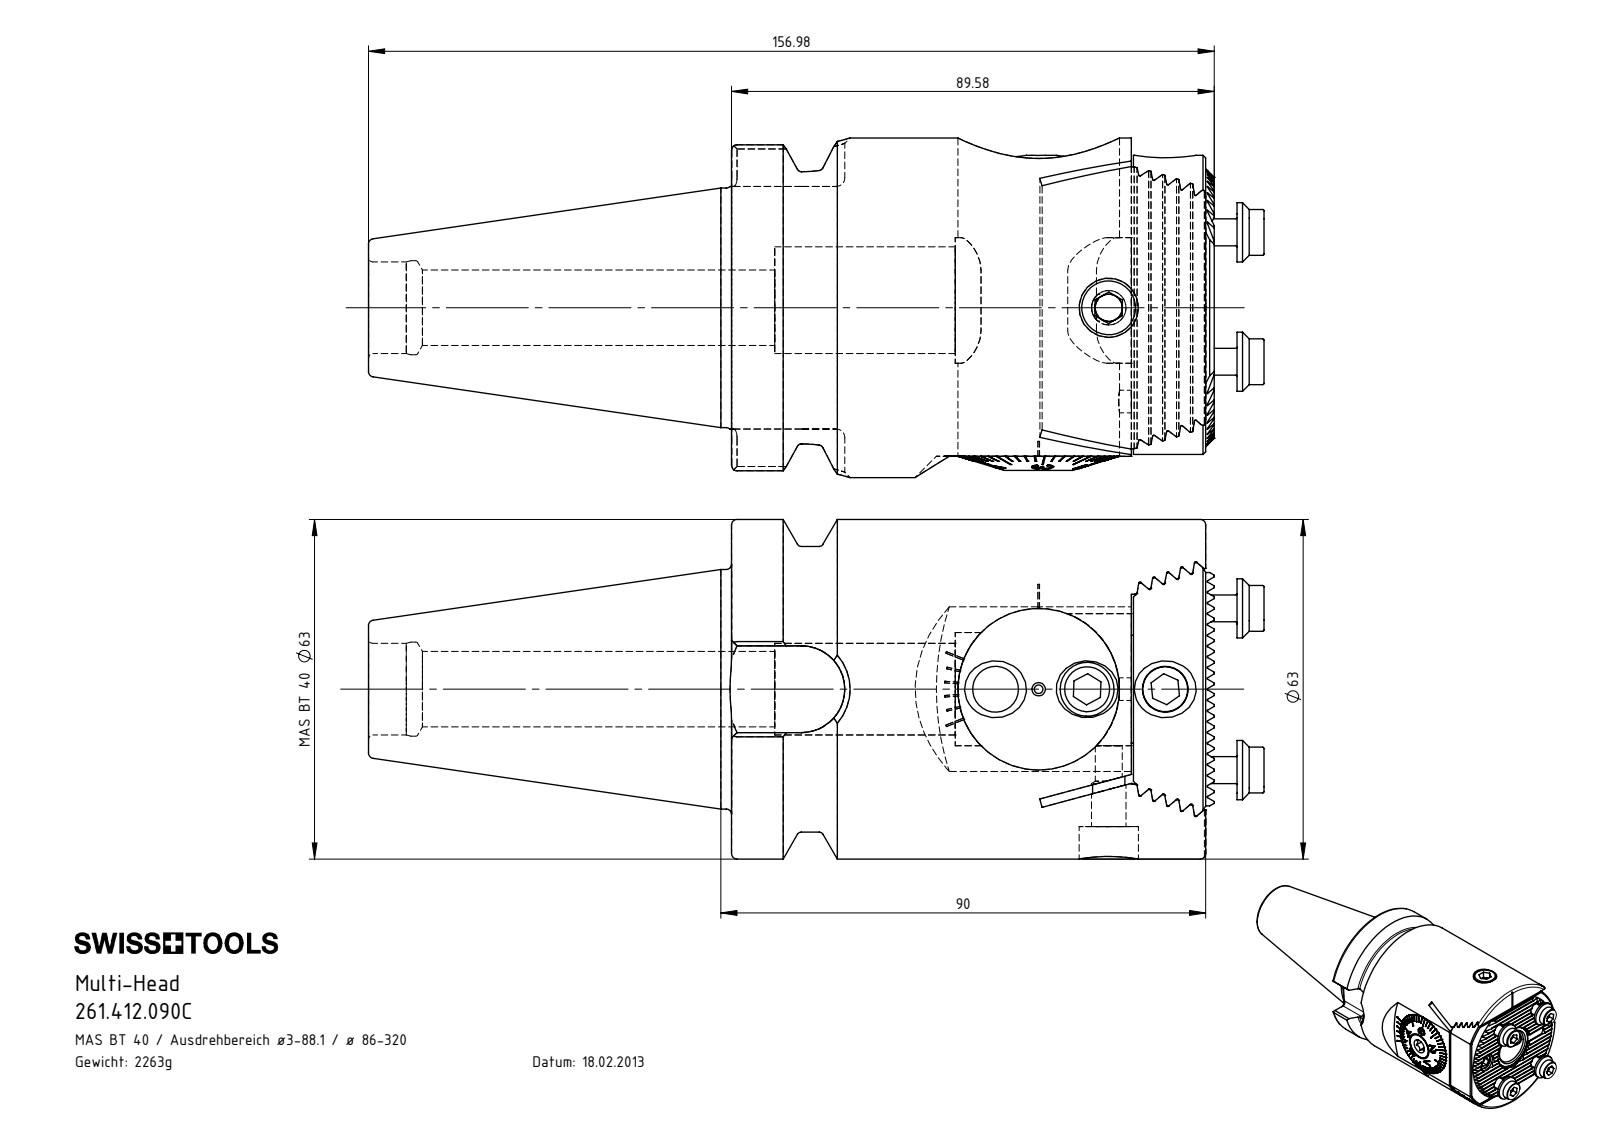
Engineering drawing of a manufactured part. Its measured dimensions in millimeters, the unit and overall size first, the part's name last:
Units: millimetres
Overall size (bounding box): 166.24 × 63 × 63
Round holes (diameter × count): ⌀4.2 ×5, ⌀8.5 ×4, ⌀6.8 ×3, ⌀11 ×3, ⌀14 ×2, ⌀20 ×2, ⌀1 ×1, ⌀1.6 ×1, ⌀3.3 ×1, ⌀5 ×1, ⌀6.4 ×1, ⌀8 ×1
Round bosses / shafts (diameter × count): ⌀11 ×4, ⌀8.5 ×4, ⌀5 ×4, ⌀10 ×3, ⌀63 ×1, ⌀53 ×1, ⌀44.45 ×1, ⌀30 ×1
Partial cylindrical surfaces — rounded edges, fillets, slot ends (radius × count): R0.14 ×21, R0.2 ×20, R1.6 ×8, R6 ×6, R4 ×2, R31 ×2, R2 ×1, R7 ×1
Main face-to-face distances: 2.38, 0.4, 1.73, 4.77, 4.76, 8.66, 74.2, 74.6, 7.15, 5.2
Hole centre spacings: 16.73, 18.03, 20.52, 24, 30, 34.8, 38.42, 7.28
Volume: 288 156 mm³ · Surface area: 75 895 mm²
Bodies: 18 solids, 1198 faces (601 planar, 266 cylindrical, 331 other)
Part name (STEP PRODUCT): ISO 4026 - M10 x 20; ISO 4026 - M4 x 5; MH1-BG3.001.042_D; MH1-BG2.001.056_D (+8 more)
STEP written by: SolidWorks 2017 (CONFIG_CONTROL_DESIGN)
